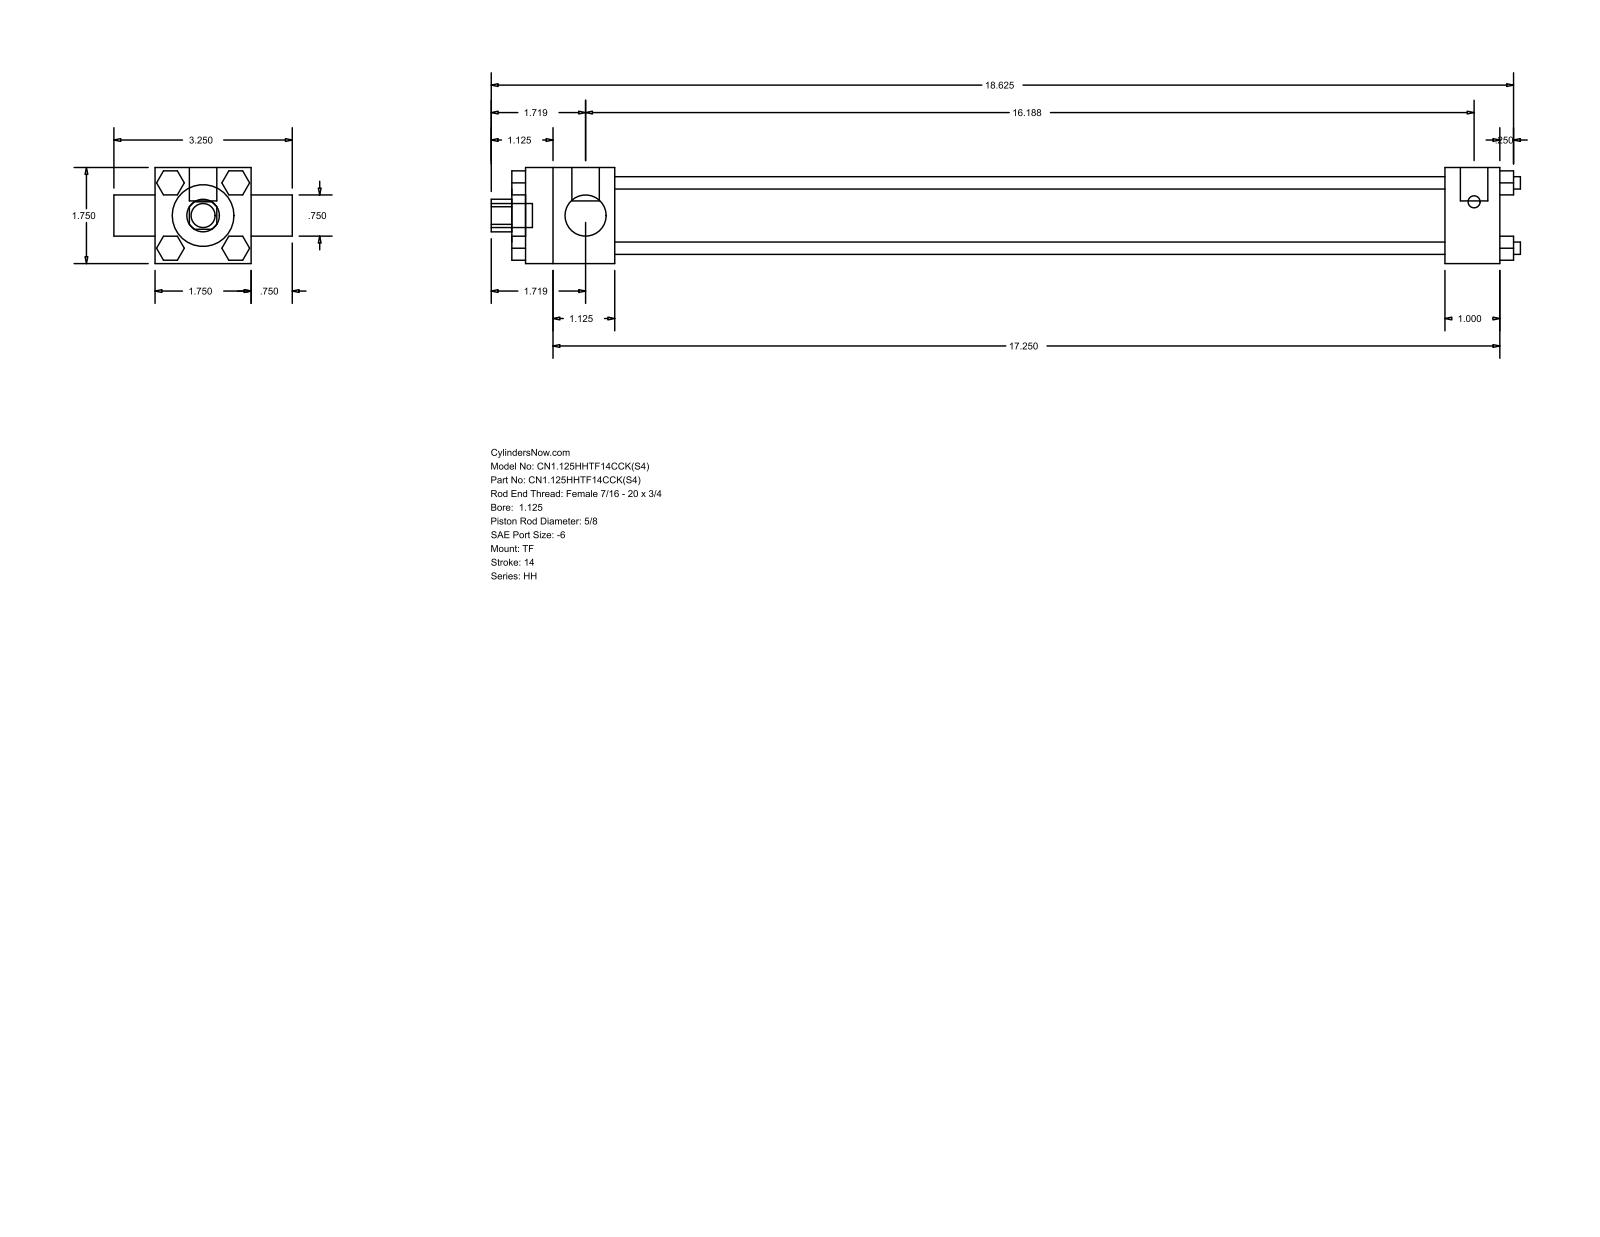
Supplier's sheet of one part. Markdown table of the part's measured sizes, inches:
| quantity | value |
| --- | --- |
| part name | HH_TF__0112_0.625 |
| STEP written by | GSSL Pune (CONFIG_CONTROL_DESIGN) |
| units | inches |
| bodies | 0 solids, 120 faces (92 planar, 28 cylindrical, 0 other) |
| overall size | 18.75 × 3.25 × 1.75 |
| round holes (diameter × count) | 0.625 × 1, 0.75 × 1, 1.125 × 1, 1.375 × 1 |
| round bosses / shafts (diameter × count) | 0.225 × 4, 0.219 × 3, 0.5 × 2, 0.437 × 1 |
| partial cylindrical surfaces (radius × count) | 0.297 × 1 |
| main face-to-face distances | 1.75, 0.437, 15.125, 16.125, 1, 1.625, 16.75, 17.75, 1.875, 18 |
